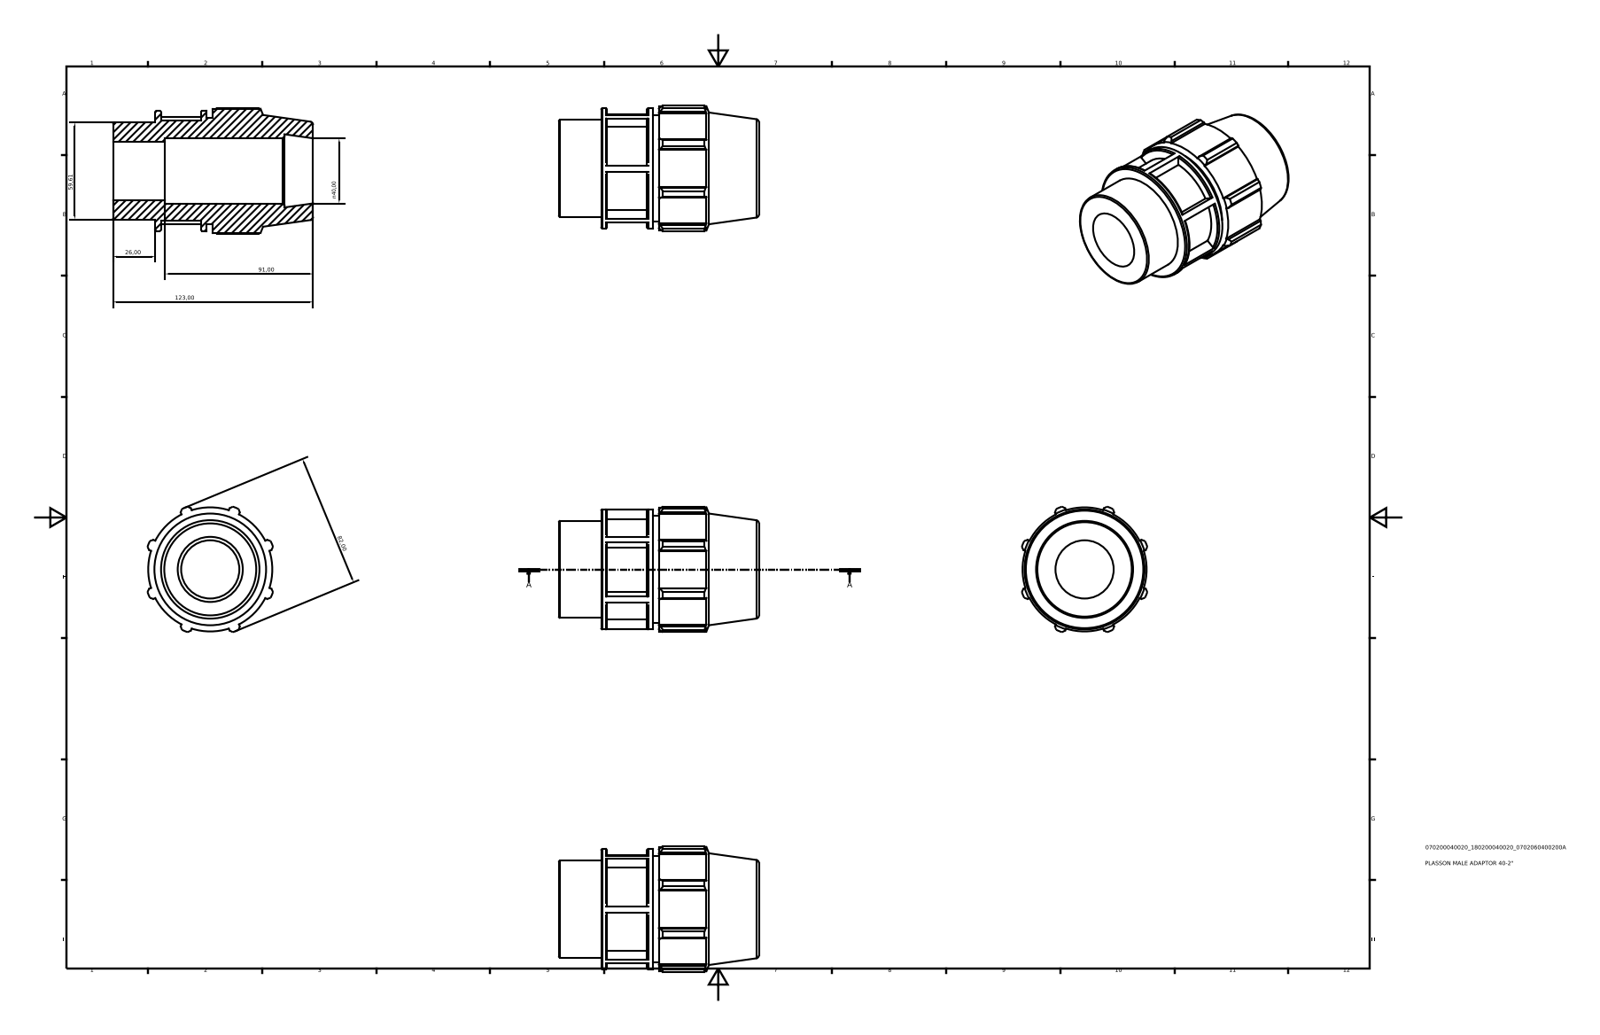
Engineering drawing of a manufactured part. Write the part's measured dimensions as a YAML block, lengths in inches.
part_name: "070200040020_180200040020"
step_written_by: "Autodesk Inventor 2015 (AUTOMOTIVE_DESIGN)"
units: inches
bodies: {solids: 1, faces: 117, planar: 63, cylindrical: 27, other: 27}
overall_size: [4.843, 3.038, 3.038]
volume: 17.48
surface_area: 83.26
round_holes:
  - {diameter: 1.408, count: 1}
  - {diameter: 1.575, count: 1}
round_bosses_or_shafts:
  - {diameter: 2.906, count: 1}
  - {diameter: 2.583, count: 1}
  - {diameter: 2.421, count: 1}
  - {diameter: 2.347, count: 1}
partial_cylinders:
  - {radius: 1.501, count: 1}
  - {radius: 1.614, count: 1}
face_to_face_distances: [2.421, 1.024, 4.843, 3.819, 1.398, 2.13, 1.107, 0.291, 2.712, 1.162]
